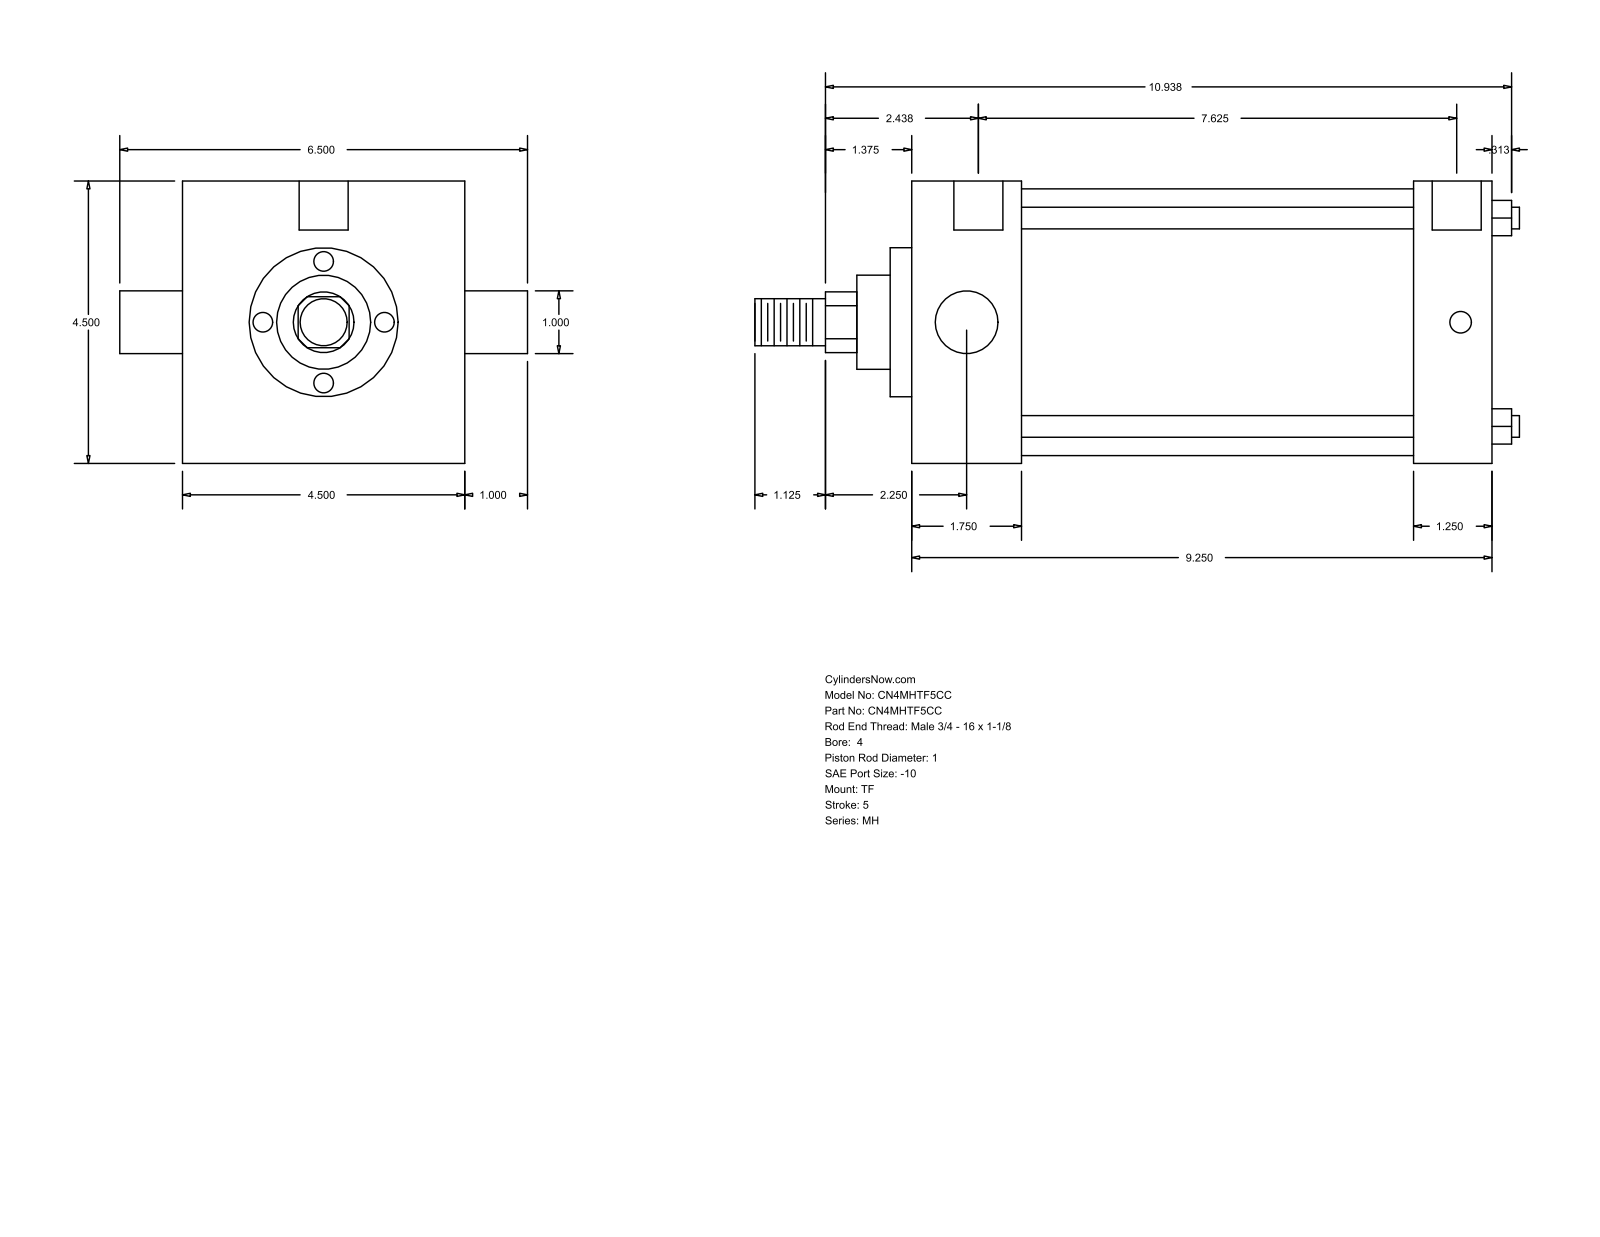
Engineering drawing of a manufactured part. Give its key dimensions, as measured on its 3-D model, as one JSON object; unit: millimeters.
{"part_name": "MH_TF__0400_1", "step_written_by": "GSSL Pune (CONFIG_CONTROL_DESIGN)", "units": "millimeters", "bodies": {"solids": 0, "faces": 86, "planar": 61, "cylindrical": 25, "other": 0}, "overall_size": [309.56, 165.1, 114.3], "round_holes": [[8.73, 3], [19.84, 2]], "round_bosses_or_shafts": [[8.76, 4], [25.4, 2], [107.95, 1], [60.33, 1], [38.1, 1], [19.05, 1]], "partial_cylinders_radius": [[12.29, 1]], "face_to_face_distances": [114.3, 234.96, 44.46, 190.5, 203.2, 158.74, 31.76, 8.73, 53.19, 211.93], "hole_center_spacings": [1.58, 1.59, 193.68, 195.26, 195.27, 196.85]}
